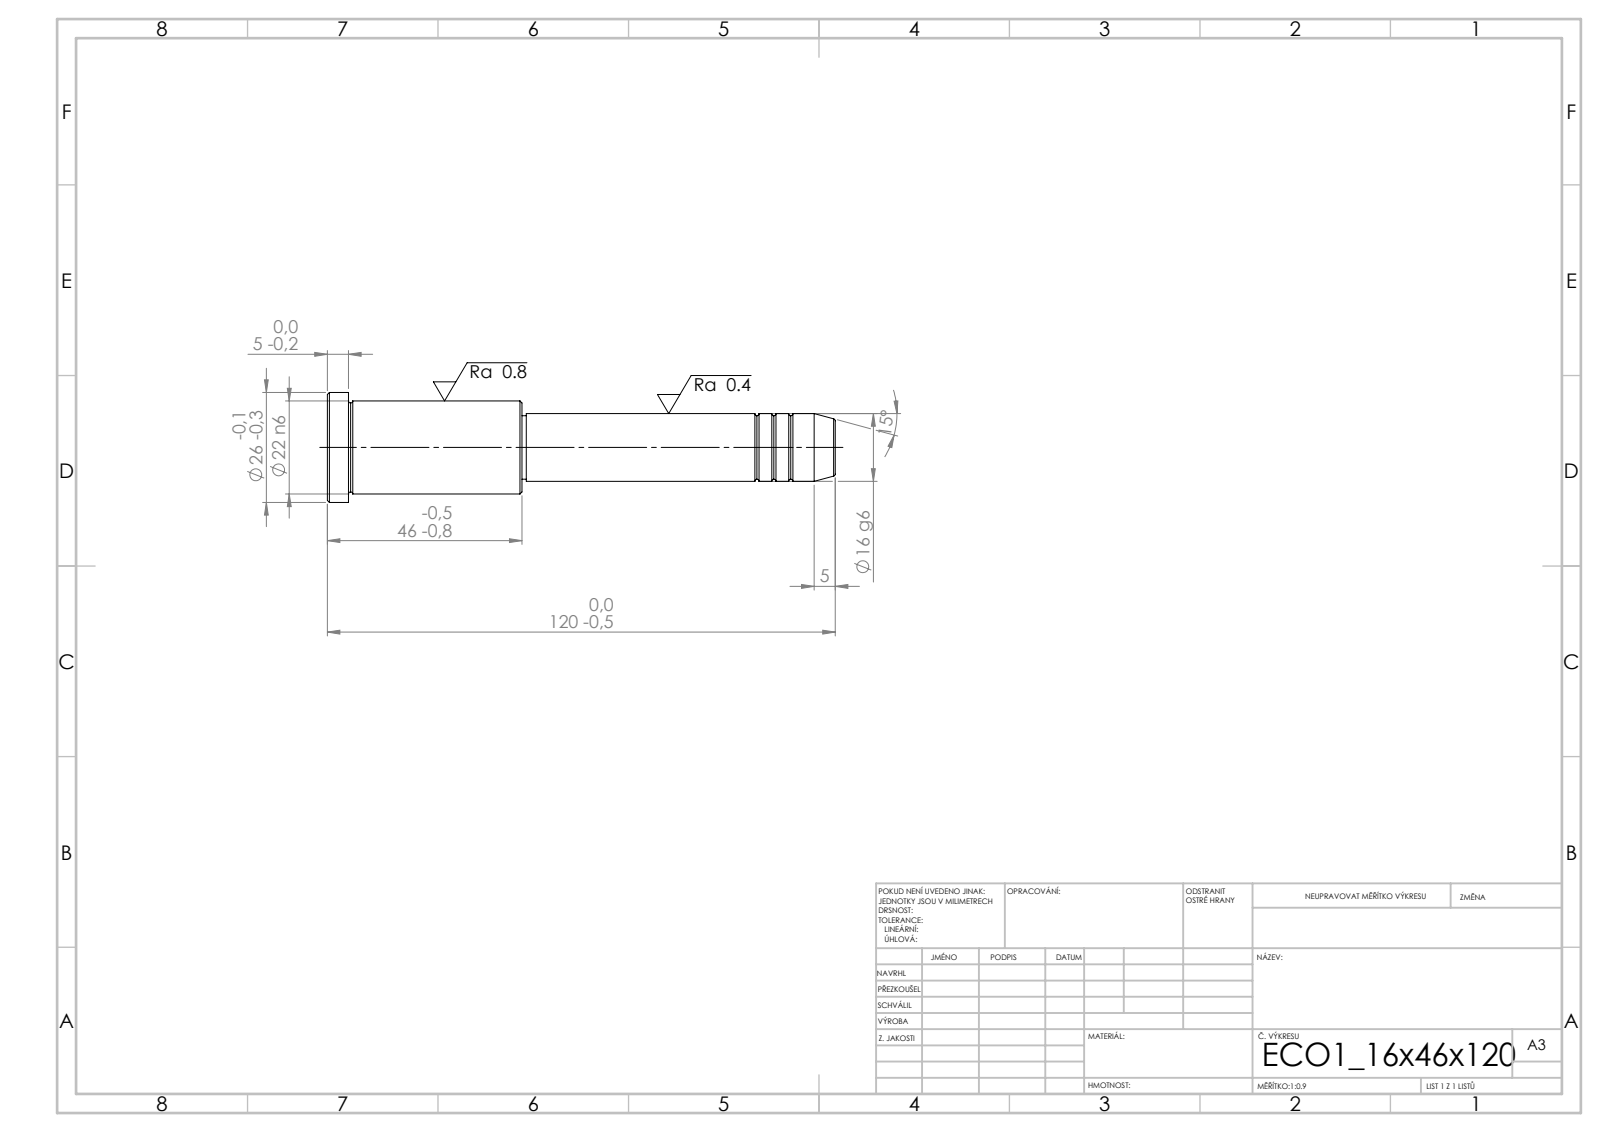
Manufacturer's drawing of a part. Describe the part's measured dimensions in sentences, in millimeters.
Its 3-D file was written by "SolidWorks 2019 (CONFIG_CONTROL_DESIGN)". It is 1 solid with 43 faces: 5 planar, 14 cylindrical and 24 other. Overall it measures 120 by 26 by 26 millimeters. Its volume is 32 831 cubic millimeters and its surface area 8 058 square millimeters. Round bosses or shafts: 1 of diameter 26, 1 of diameter 22, 1 of diameter 16, 1 of diameter 15. The main face-to-face distances are 46, 41, 5, 74, 115, 120, 73, 1, 42, 47.
